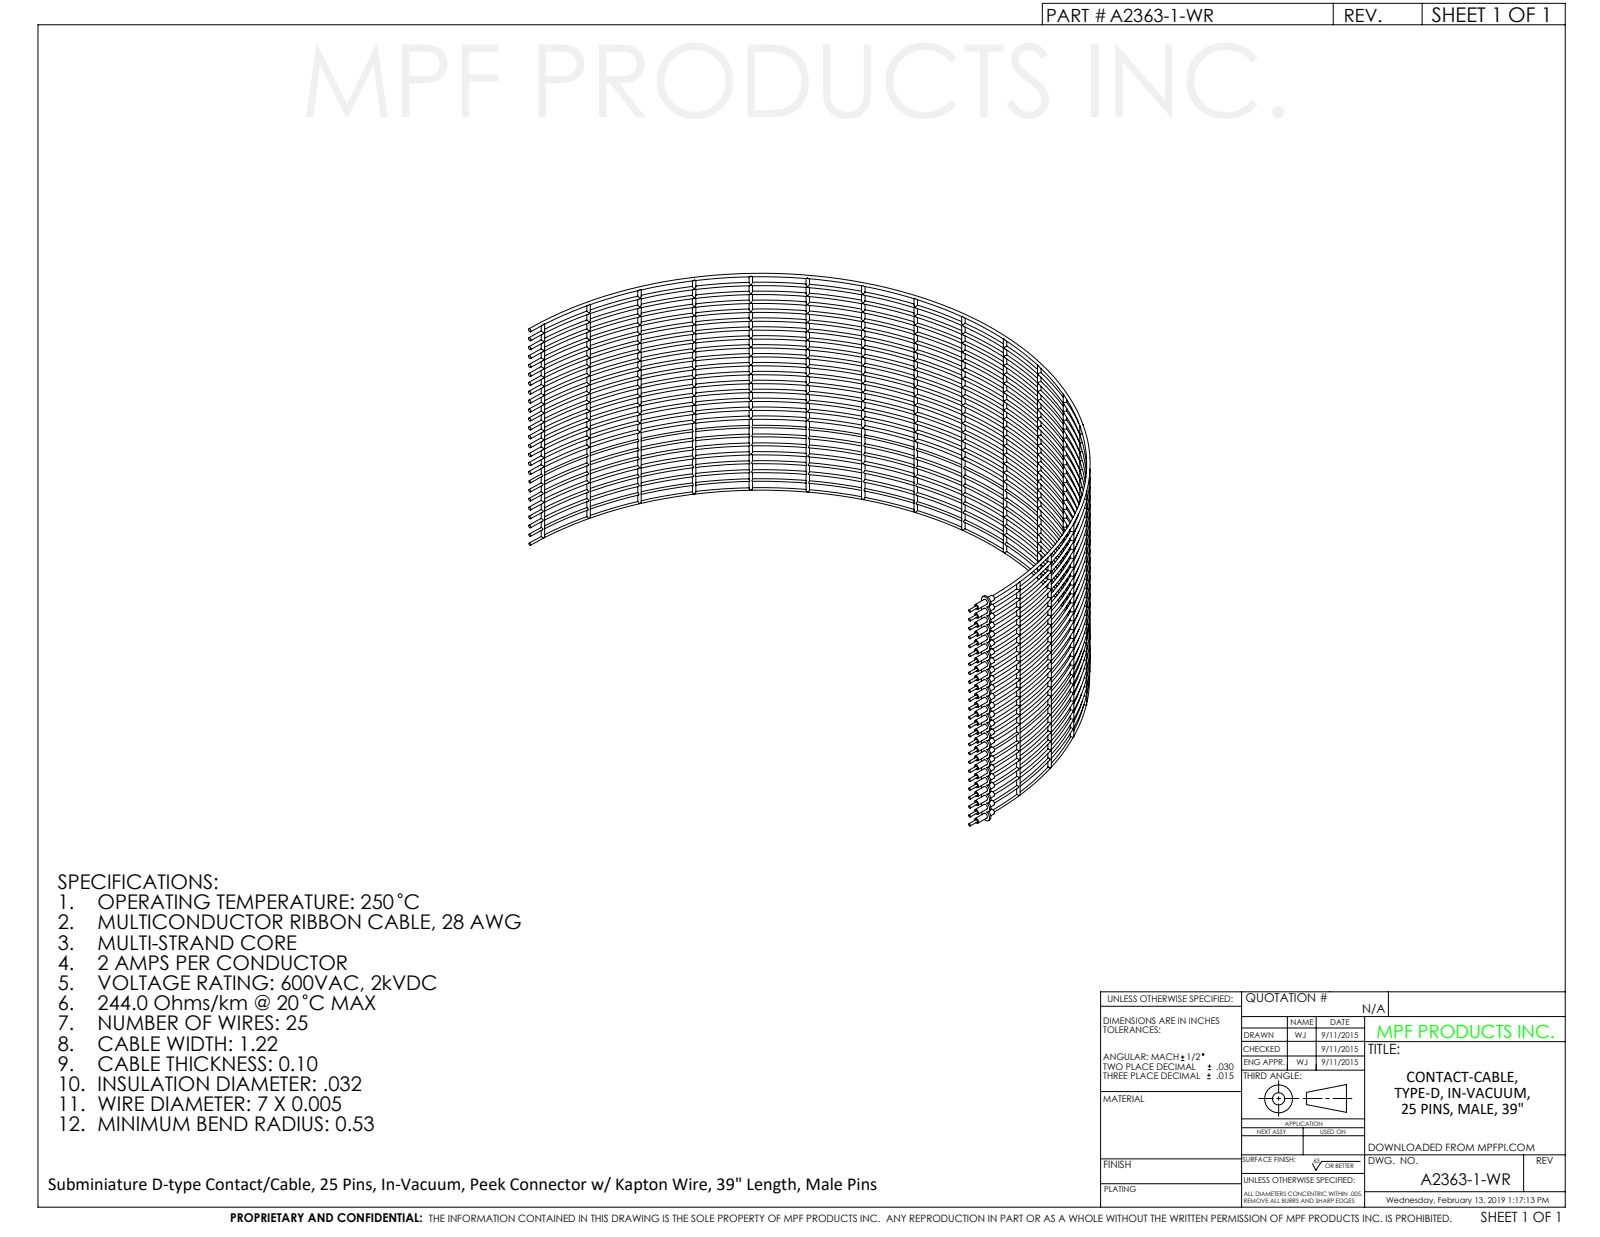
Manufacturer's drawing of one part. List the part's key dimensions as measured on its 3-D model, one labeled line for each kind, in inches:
Part name (STEP PRODUCT): A2363-1-WR
STEP written by: SolidWorks 2012 (CONFIG_CONTROL_DESIGN)
Units: inches
Bodies: 1 solid, 1883 faces (139 planar, 816 cylindrical, 928 other)
Overall size (bounding box): 6.069 × 3.315 × 2.505
Volume: 0.205 in³ · Surface area: 26.16 in²
Round bosses / shafts (diameter × count): ⌀0.05 ×25, ⌀0.023 ×25, ⌀0.105 ×24, ⌀0.032 ×18
Partial cylindrical surfaces — rounded edges, fillets, slot ends (radius × count): R0.053 ×1
Main face-to-face distances: 0.018, 0.074, 0.091, 0.207, 0.134, 0.116, 0.298, 0.225, 0.207, 0.091
